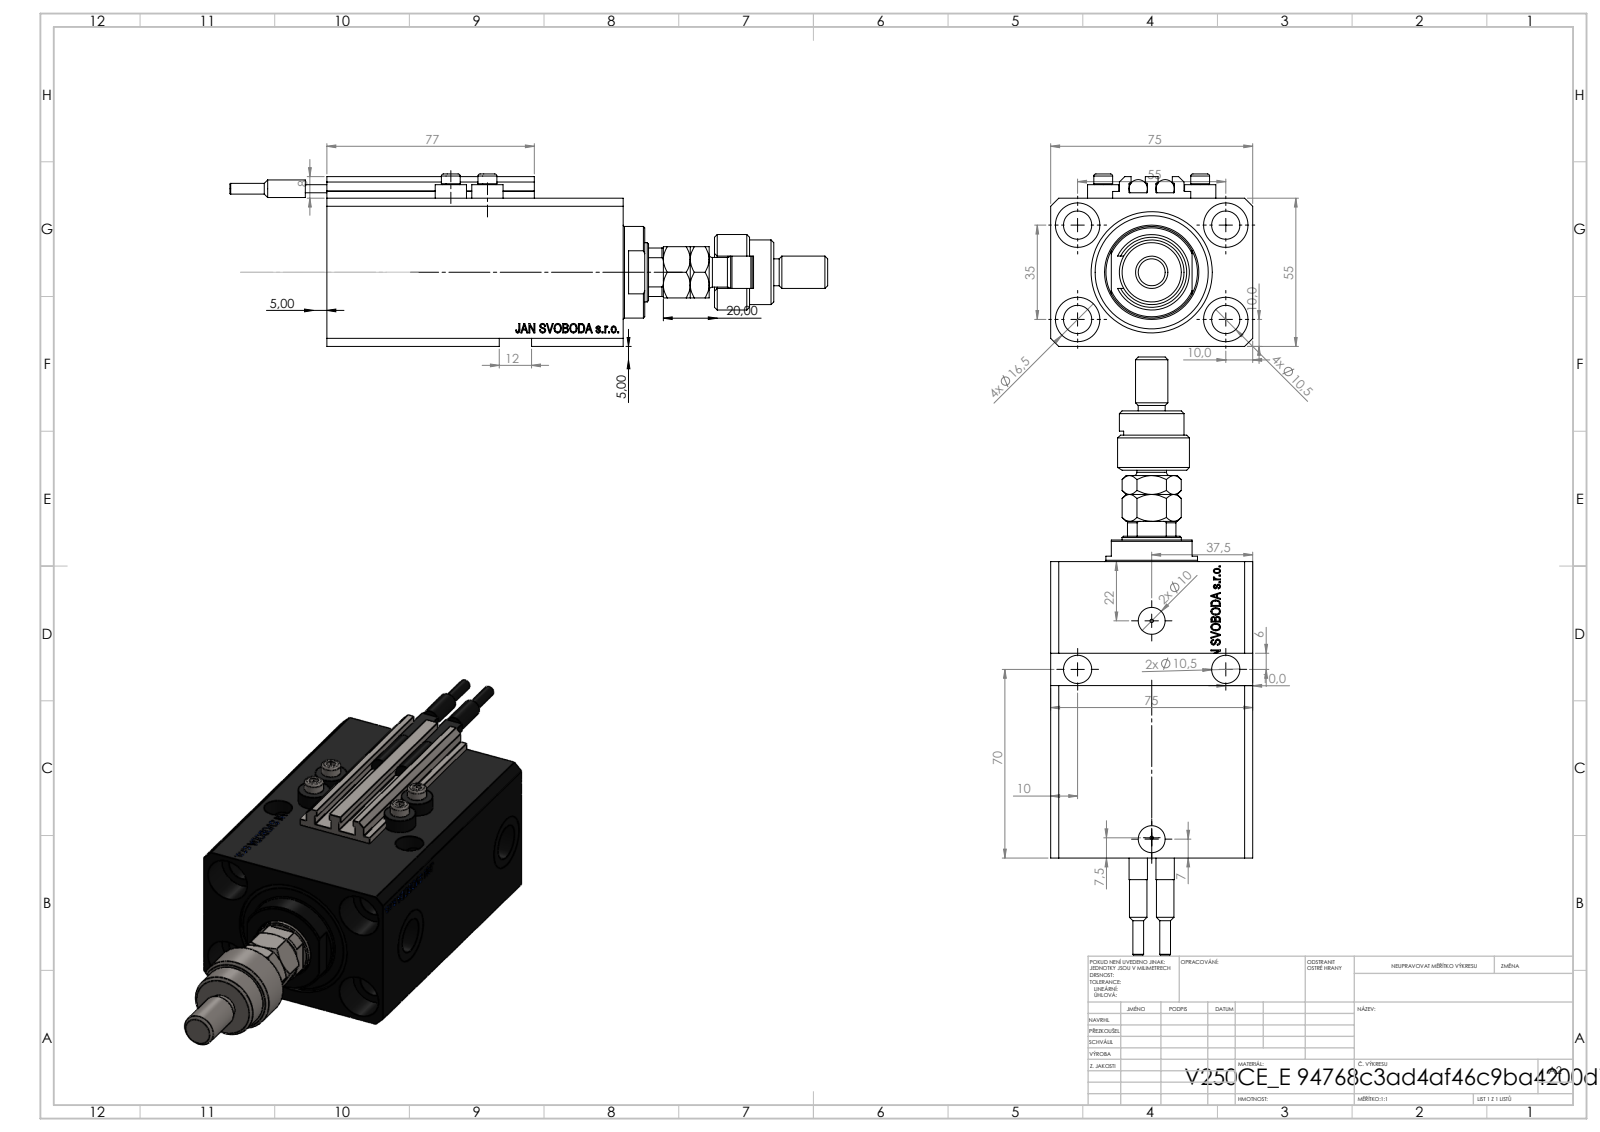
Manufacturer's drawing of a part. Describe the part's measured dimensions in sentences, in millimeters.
The part is named "V250CE_VC_E; MFA; FEMALE_PART_FOR_DFA; V250CE_C_VCP (+3 more)". Its 3-D file was written by "SolidWorks 2019 (CONFIG_CONTROL_DESIGN)". It is 12 solids with 1221 faces: 574 planar, 171 cylindrical and 476 other. Overall it measures 222 by 75 by 64 millimeters. Its volume is 402 791 cubic millimeters and its surface area 105 514 square millimeters. Round holes: 9 of diameter 10.5, 4 of diameter 1.25, 4 of diameter 4, 4 of diameter 16.5, 2 of diameter 10, 2 of diameter 13.16, 2 of diameter 20, 1 of diameter 22, 1 of diameter 32, 1 of diameter 45. Round bosses or shafts: 4 of diameter 11.6, 4 of diameter 7, 2 of diameter 6.8, 2 of diameter 6.5, 2 of diameter 4, 1 of diameter 34, 1 of diameter 28, 1 of diameter 24. Partial cylindrical surfaces (rounded edges, fillets, slot ends): 10 of radius 0.2, 1 of radius 9.75, 1 of radius 10.5. The main face-to-face distances are 55, 75, 15, 3, 110, 57, 95, 9.9, 8, 19. The hole center spacings are 32.6, 32.87, 55, 68.74, 13.6, 14.09, 23.05, 25.81.
